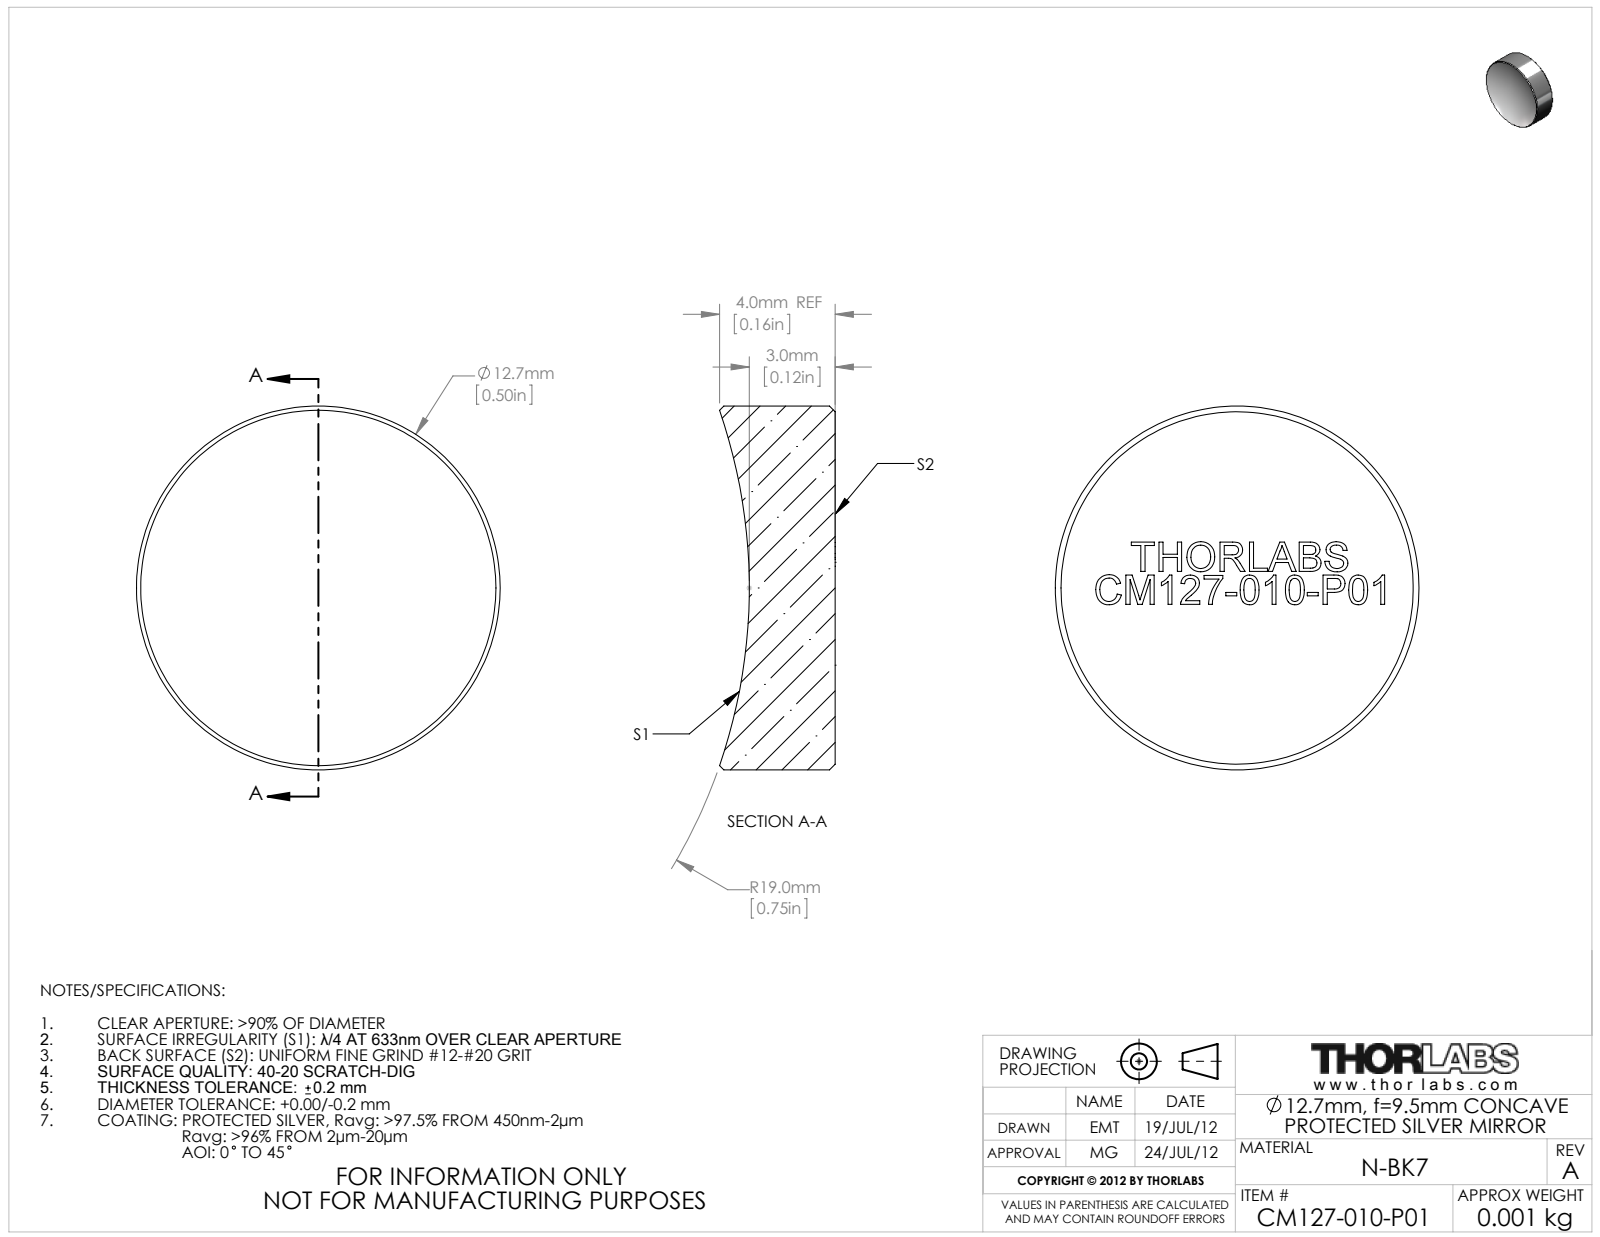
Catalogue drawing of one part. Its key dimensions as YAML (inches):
part_name: "24628-E0W"
step_written_by: "SolidWorks 2011 (CONFIG_CONTROL_DESIGN)"
units: inches
bodies: {solids: 0, faces: 39, planar: 31, cylindrical: 2, other: 6}
overall_size: [0.5, 0.5, 0.159]
round_bosses_or_shafts:
  - {diameter: 0.5, count: 1}
